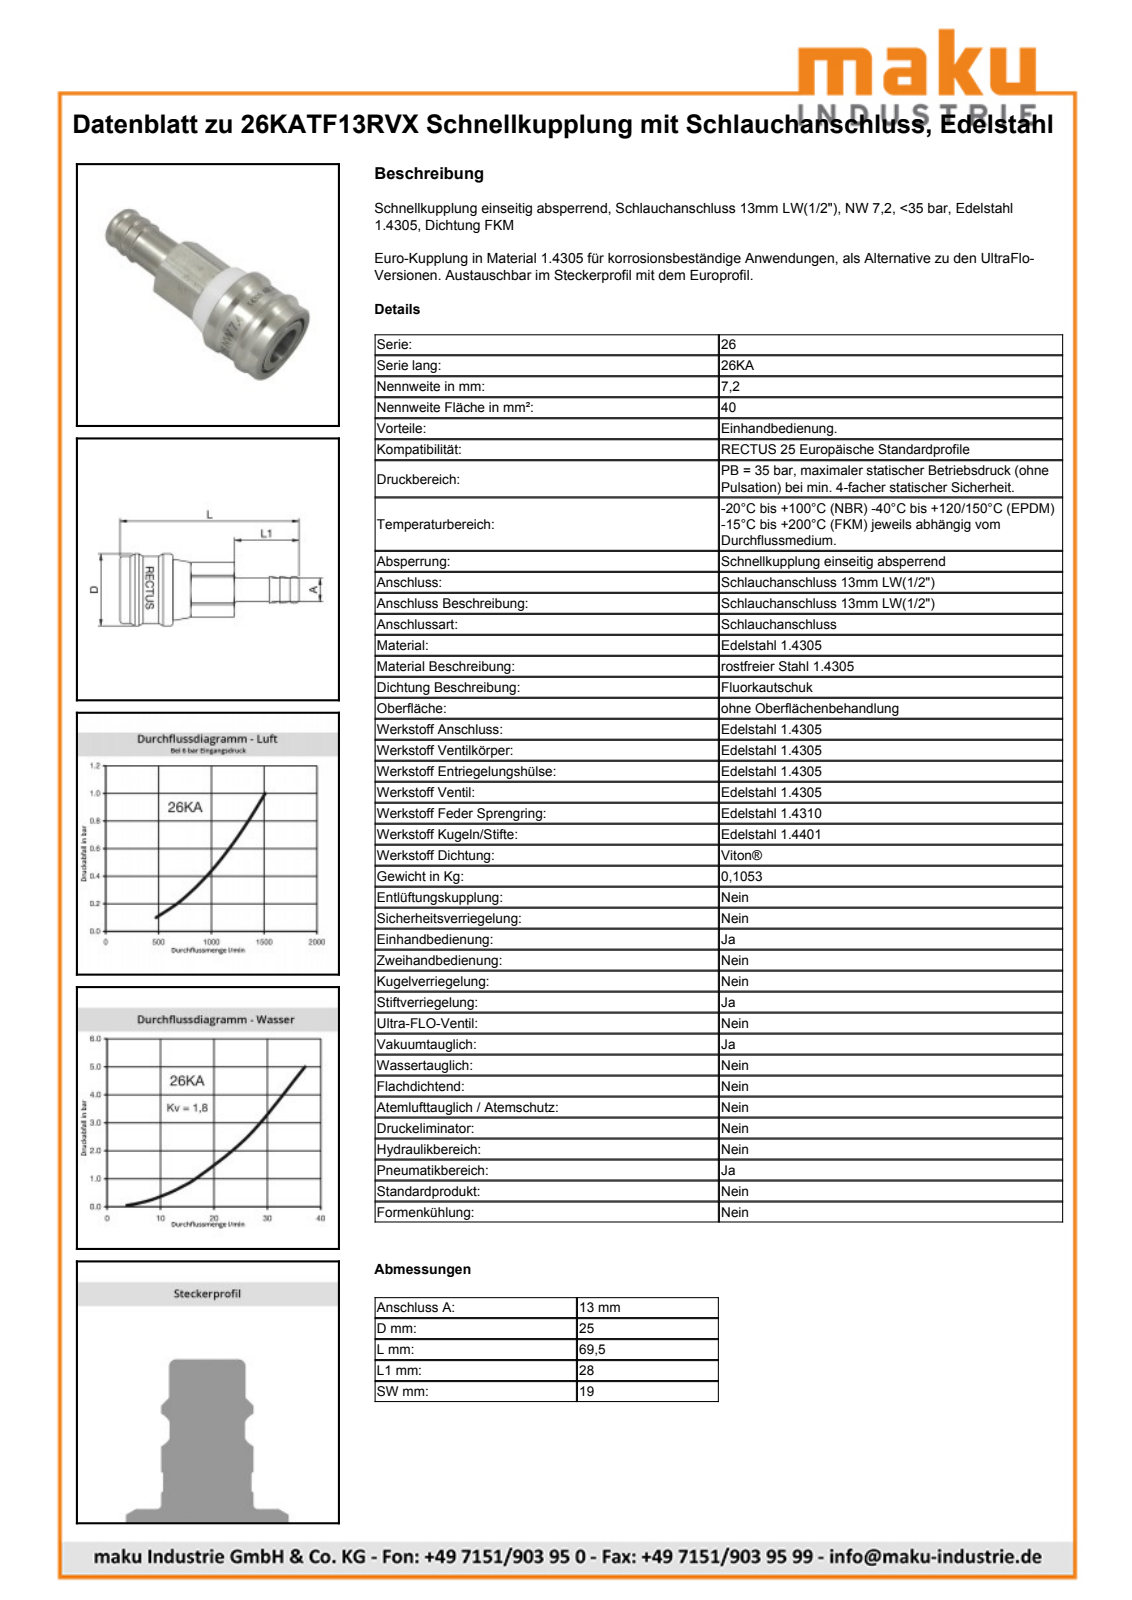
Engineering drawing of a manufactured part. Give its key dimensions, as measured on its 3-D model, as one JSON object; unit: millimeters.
{"part_name": "D105881", "step_written_by": "Autodesk Inventor 2011 (AUTOMOTIVE_DESIGN)", "units": "millimeters", "bodies": {"solids": 2, "faces": 584, "planar": 222, "cylindrical": 82, "other": 280}, "overall_size": [69.51, 28, 28], "volume_mm3": 20212, "surface_area_mm2": 10434, "round_holes": [[15.1, 1], [16, 1], [19.15, 1], [20, 1], [21.2, 1], [24, 1]], "round_bosses_or_shafts": [[28, 1], [26, 1], [23.8, 1], [21, 1], [18.95, 1], [18, 1], [16.65, 1], [15.2, 1]], "partial_cylinders_radius": [[10.7, 1], [12.9, 1]], "face_to_face_distances": [19, 5.99, 69.5, 63.51, 6, 69.51, 20.5, 44.51, 44.5, 38.51]}
